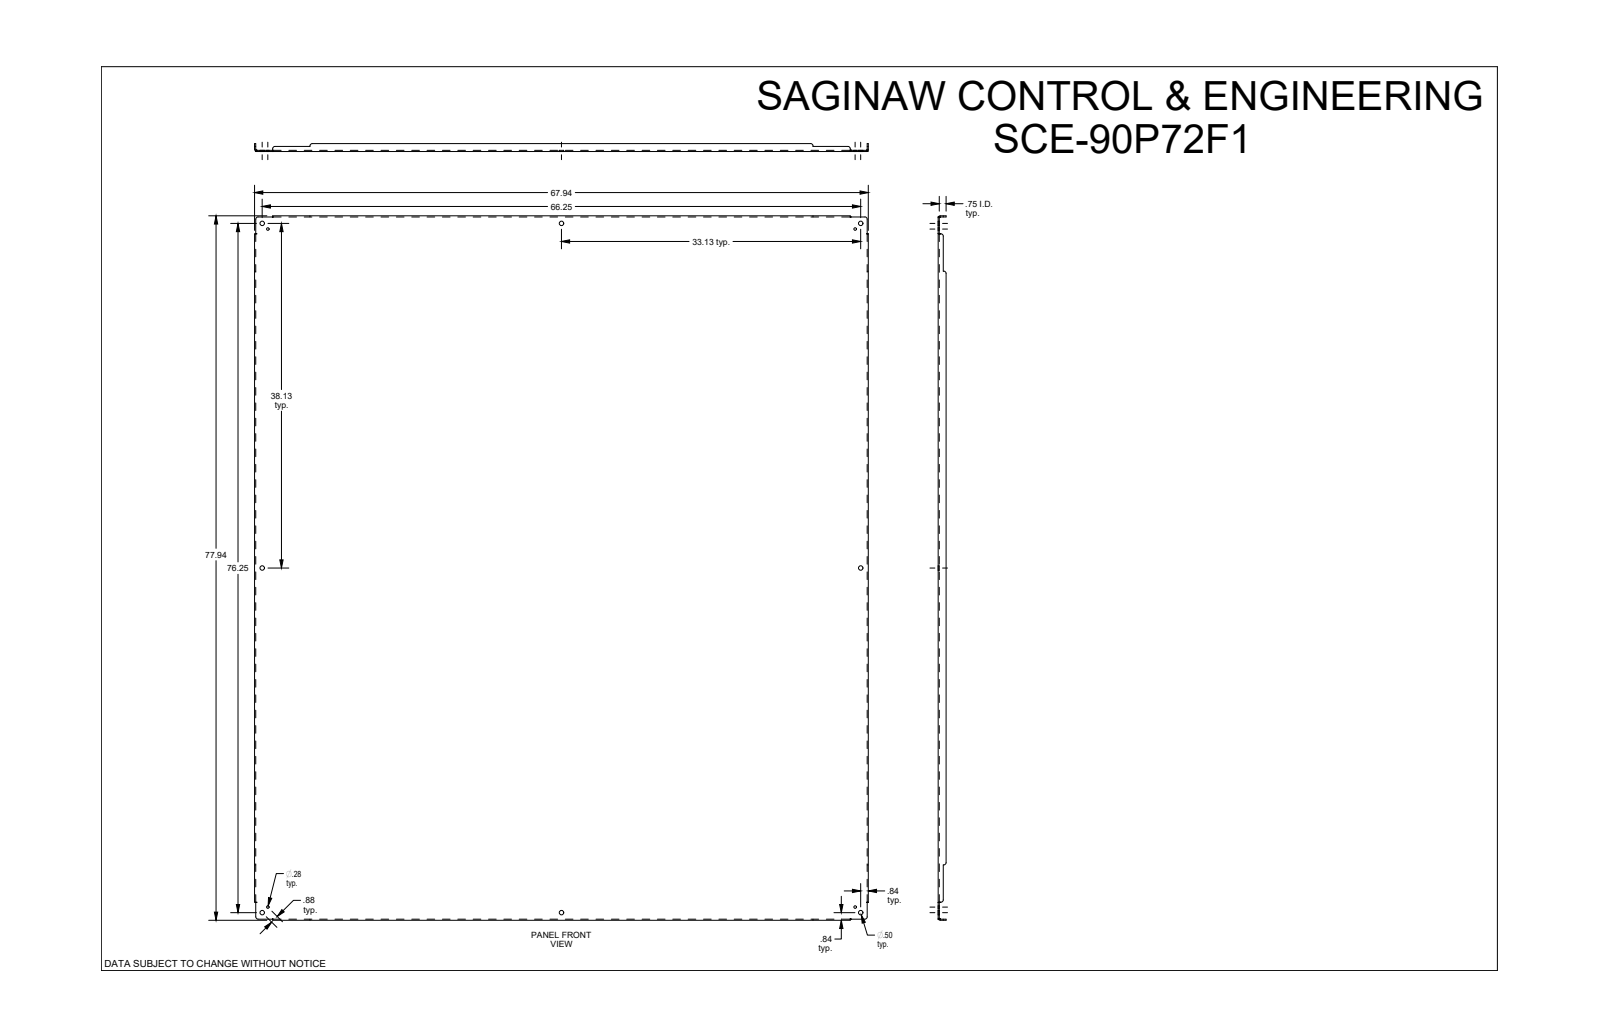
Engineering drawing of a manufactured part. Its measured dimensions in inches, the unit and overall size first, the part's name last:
Units: inches
Overall size (bounding box): 77.938 × 67.938 × 0.875
Round holes (diameter × count): ⌀0.5 ×8, ⌀0.281 ×4
Partial cylindrical surfaces — rounded edges, fillets, slot ends (radius × count): R0.25 ×12, R0.112 ×4, R0.237 ×4
Main face-to-face distances: 0.125, 0.125, 67.813, 77.813, 67.687, 67.938, 77.687, 77.938, 0.75, 0.875
Hole centre spacings: 0.875, 32.512, 33.125, 37.511, 38.125, 50.506, 65.634, 75.593
Volume: 683.3 in³ · Surface area: 10 972 in²
Bodies: 1 solid, 110 faces (46 planar, 40 cylindrical, 24 other)
Part name (STEP PRODUCT): SCE-90P72F1
STEP written by: SolidWorks 2019 (AUTOMOTIVE_DESIGN)
